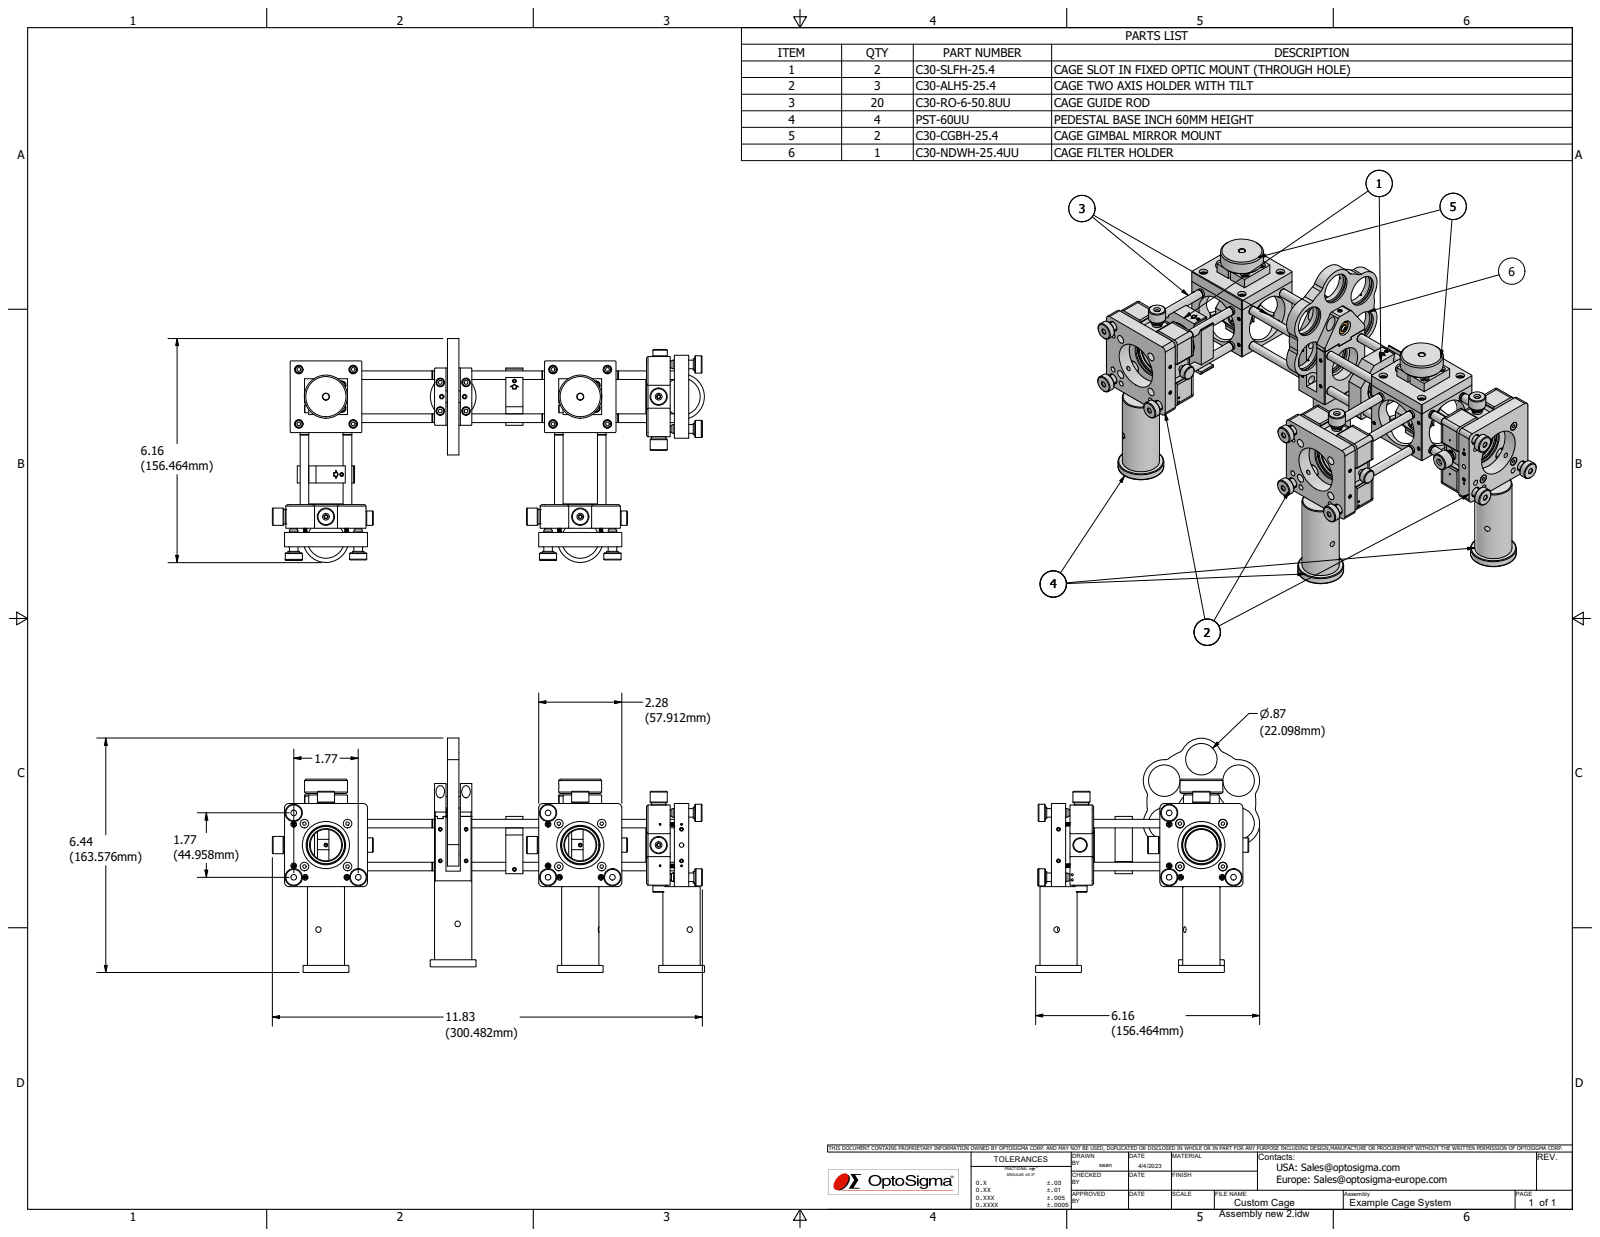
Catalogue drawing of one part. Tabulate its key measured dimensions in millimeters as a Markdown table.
| quantity | value |
| --- | --- |
| part name | Custom Cage Assembly new 2; C30-SLFH-25.4; C30-ALH5-25.4; PST-60UU (+5 more) |
| STEP written by | Autodesk Inventor 2022 (AUTOMOTIVE_DESIGN) |
| units | millimeters |
| bodies | 58 solids, 4120 faces (2168 planar, 1249 cylindrical, 703 other) |
| overall size | 301.9 × 163.7 × 156.48 |
| volume | 516 448 mm³ |
| surface area | 244 465 mm² |
| round holes (diameter × count) | 2.5 × 38, 4 × 26, 6 × 25, 1.1 × 20, 1 × 19, 3.3 × 16, 22 × 13, 2.3 × 12, 8 × 12, 1.6 × 10, 7.5 × 9, 10 × 9 |
| round bosses / shafts (diameter × count) | 1 × 20, 5.5 × 18, 12 × 14, 6 × 13, 10 × 12, 3.8 × 12, 8 × 10, 4 × 10 |
| partial cylindrical surfaces (radius × count) | 2 × 106, 0.5 × 60, 1 × 52, 4 × 28, 3 × 25, 2.2 × 24, 3.5 × 24, 1.5 × 12 |
| main face-to-face distances | 9, 10, 1, 8, 3, 17, 48, 50, 13, 16.5 |
| hole center spacings | 14, 21.21, 30, 177.6, 29, 32.65, 14.5, 14.53 |
